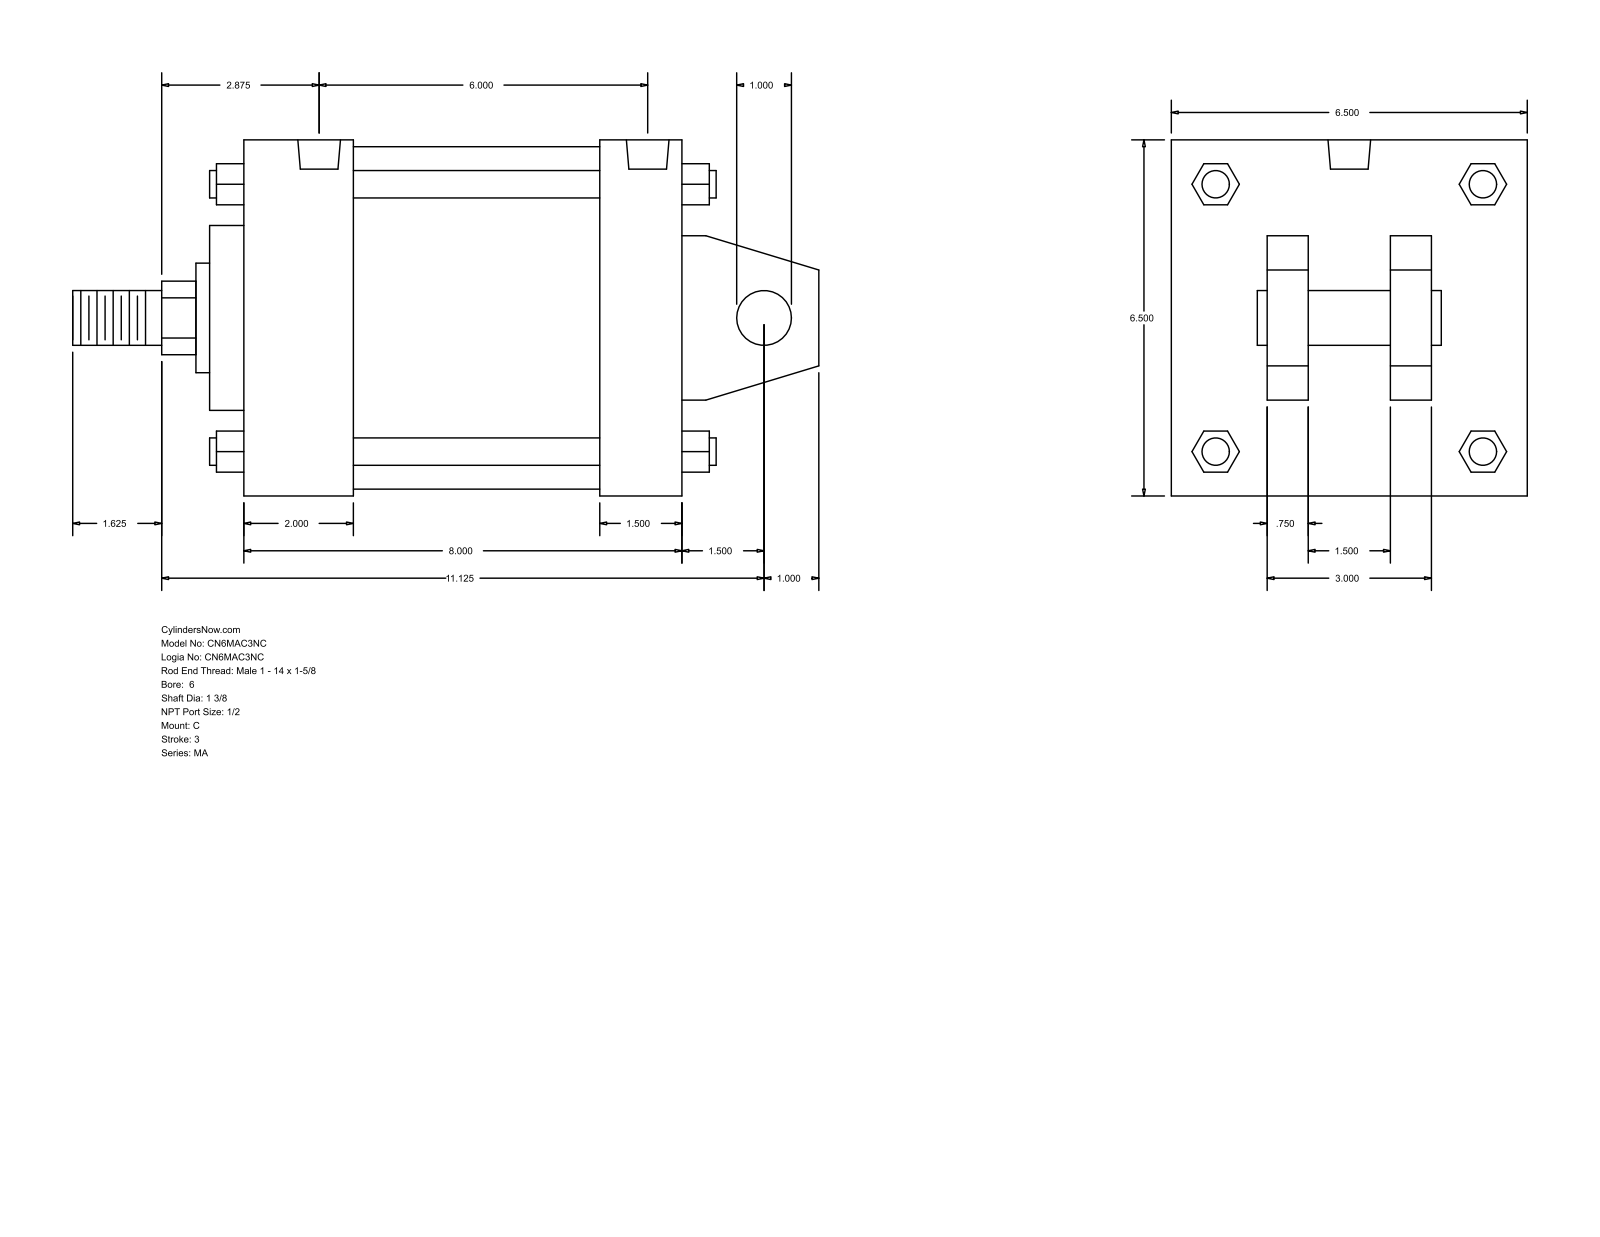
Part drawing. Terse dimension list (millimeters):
name: MA_C__0600_1.375
written by: GSSL Pune (CONFIG_CONTROL_DESIGN)
unit: mm
bodies: 0 solids, 141 faces (109 planar, 32 cylindrical, 0 other)
size: 346.07 × 165.1 × 165.1
holes: 4× ⌀17.46, 2× ⌀19.77
bosses: 4× ⌀12.7, 2× ⌀25.4, 1× ⌀158.75, 1× ⌀85.72, 1× ⌀50.8, 1× ⌀34.92
rounds: 1× R17.06
face distances: 165.1, 203.2, 38.1, 19.05, 63.5, 101.6, 50.8, 44.45, 120.65, 57.15
hole spacings: 152.4, 3.18, 149.22, 155.58
